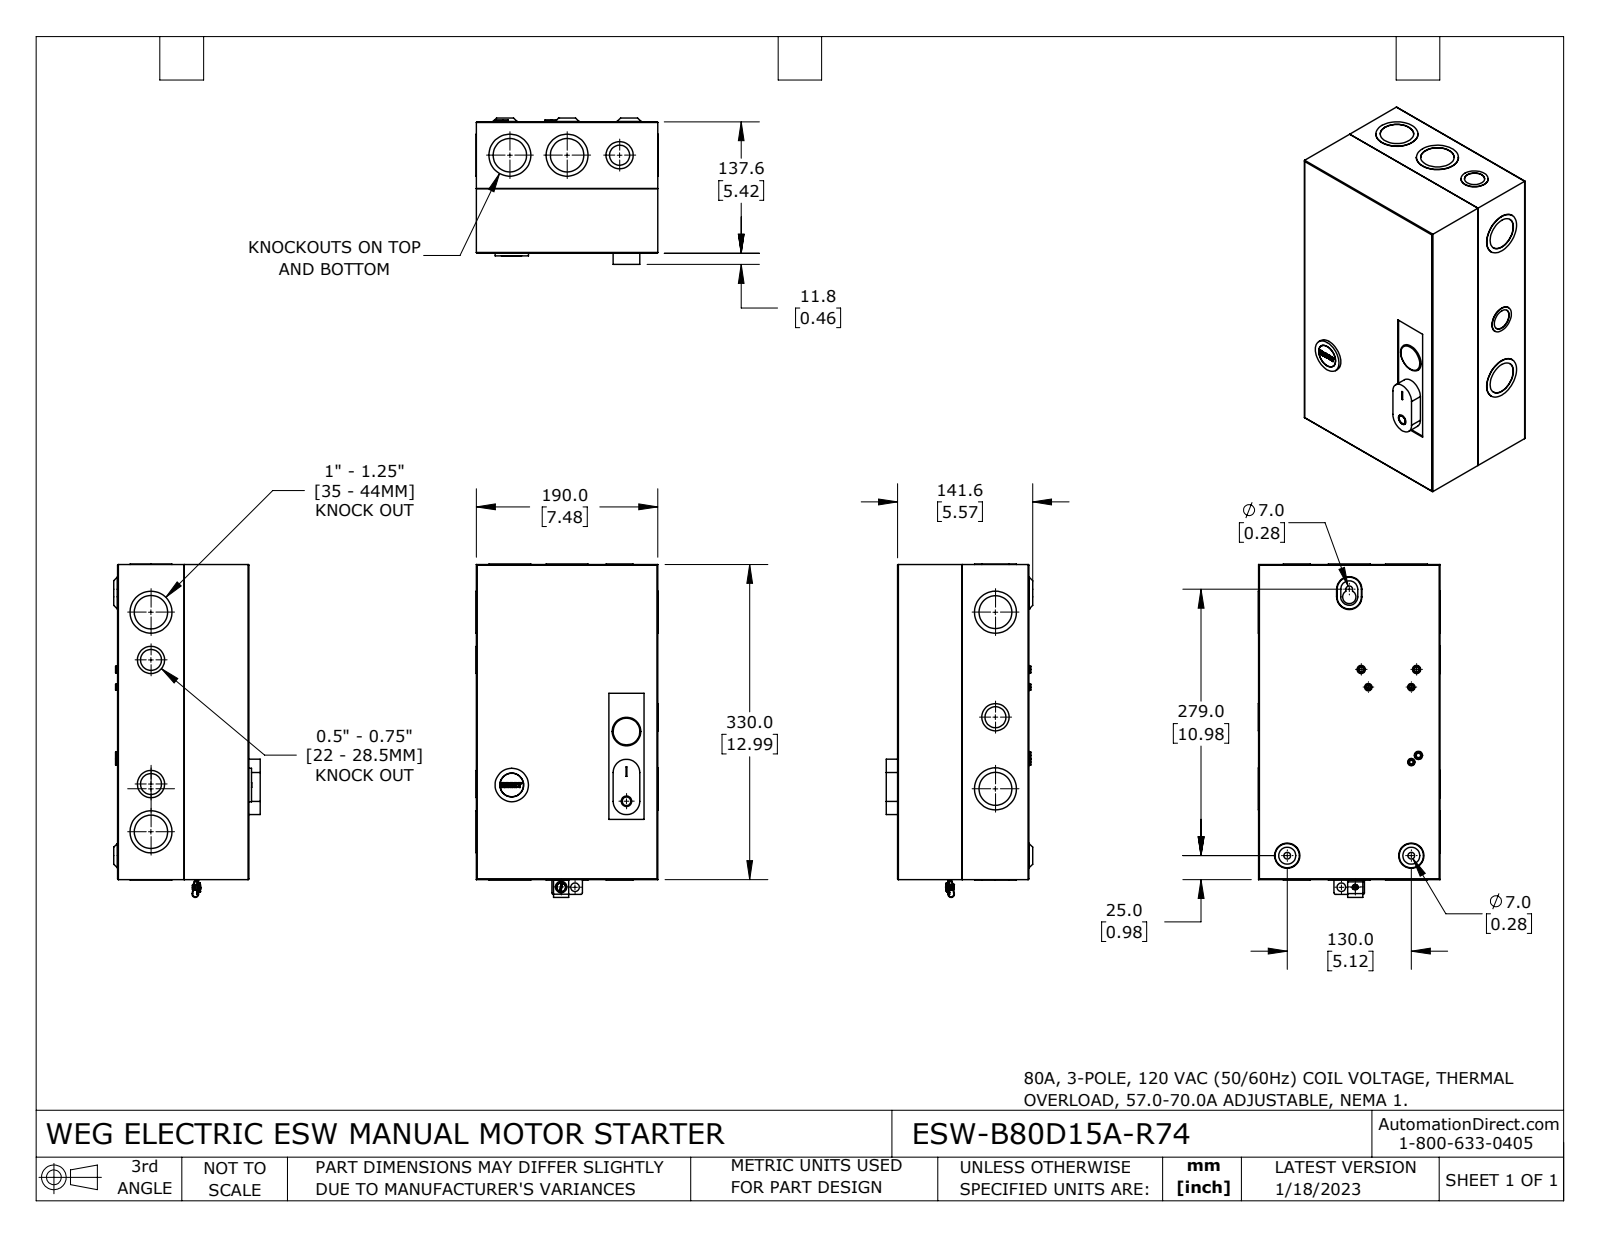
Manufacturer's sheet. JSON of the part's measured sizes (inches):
{"part_name": "ESW-B80D15A-R74", "step_written_by": "SolidWorks 2021 (CONFIG_CONTROL_DESIGN)", "units": "inches", "bodies": {"solids": 7, "faces": 435, "planar": 161, "cylindrical": 221, "other": 53}, "overall_size": [13.74, 7.504, 6.039], "volume_in3": 24.58, "surface_area_in2": 936.7, "round_holes": [[1.378, 4], [0.146, 3], [0.183, 3], [0.276, 2], [0.866, 2], [0.886, 2], [1.357, 2], [0.256, 1], [0.279, 1], [0.354, 1], [0.433, 1], [0.469, 1]], "round_bosses_or_shafts": [[1.732, 4], [1.122, 3], [0.278, 3], [0.24, 3], [1.734, 2], [1.378, 1], [1.193, 1], [1.148, 1]], "partial_cylinders_radius": [[0.004, 34], [0.031, 8], [0.079, 3], [0.138, 3], [0.059, 2], [0.075, 2], [0.108, 2], [0.122, 2]], "face_to_face_distances": [0.047, 5.37, 7.433, 5.323, 5.417, 12.945, 7.386, 7.48, 0.071, 12.898], "hole_center_spacings": [0.571, 1.772, 1.969, 2.283, 2.362, 5.118, 7.087, 10.972]}
